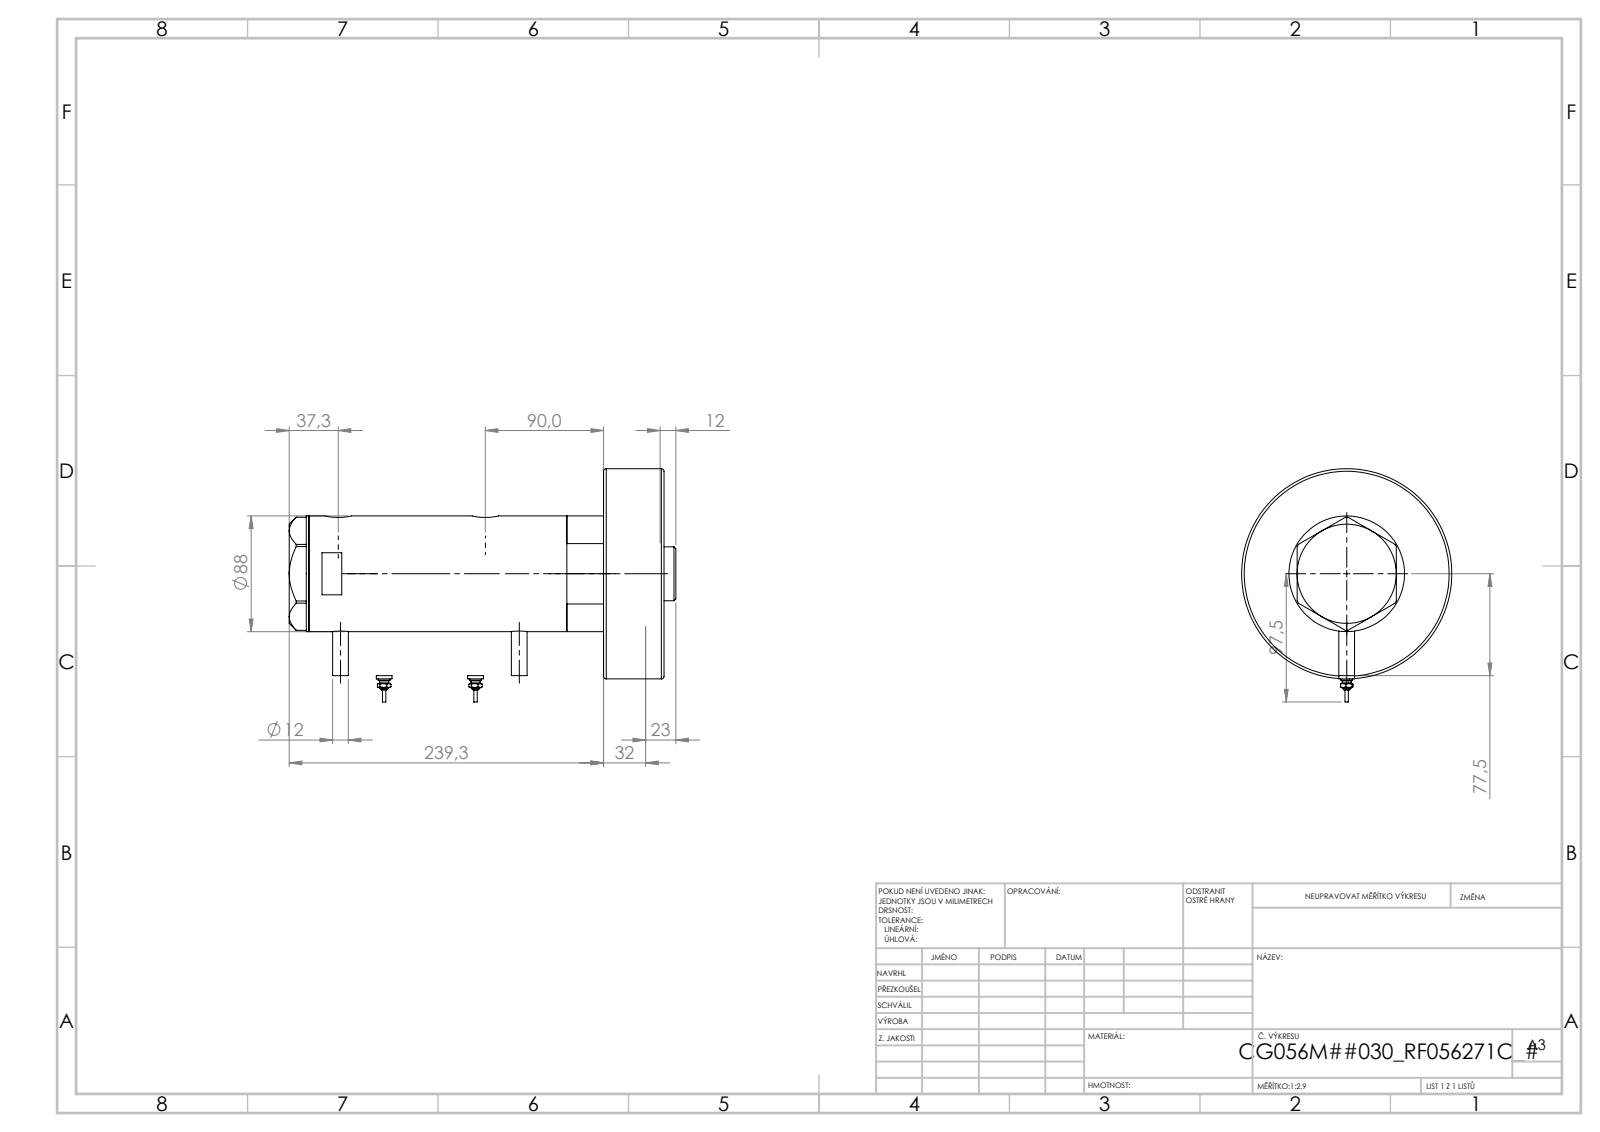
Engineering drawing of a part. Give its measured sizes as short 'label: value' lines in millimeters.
name: V270CG_MIDDLE; V270CG_FRONT; V270CG_BACK; V270CG_271C (+2 more)
written by: SolidWorks 2019 (CONFIG_CONTROL_DESIGN)
unit: mm
bodies: 7 solids, 242 faces (83 planar, 81 cylindrical, 78 other)
size: 254.47 × 160 × 160
volume: 2 036 000 mm³; area: 264 207 mm²
holes: 2× ⌀5, 2× ⌀12.5, 2× ⌀13.16, 2× ⌀20, 1× ⌀14.5, 1× ⌀42, 1× ⌀43.5, 1× ⌀56, 1× ⌀60, 1× ⌀75, 1× ⌀80
bosses: 2× ⌀12, 2× ⌀9, 2× ⌀7, 2× ⌀4.34, 2× ⌀2.4, 1× ⌀160, 1× ⌀88, 1× ⌀73
face distances: 46, 181.9, 227.9, 104.4, 77.5, 123.5, 26, 78.4, 155.9, 201.9
hole spacings: 1.7, 25.8, 80.3, 82, 106.1, 107.8
